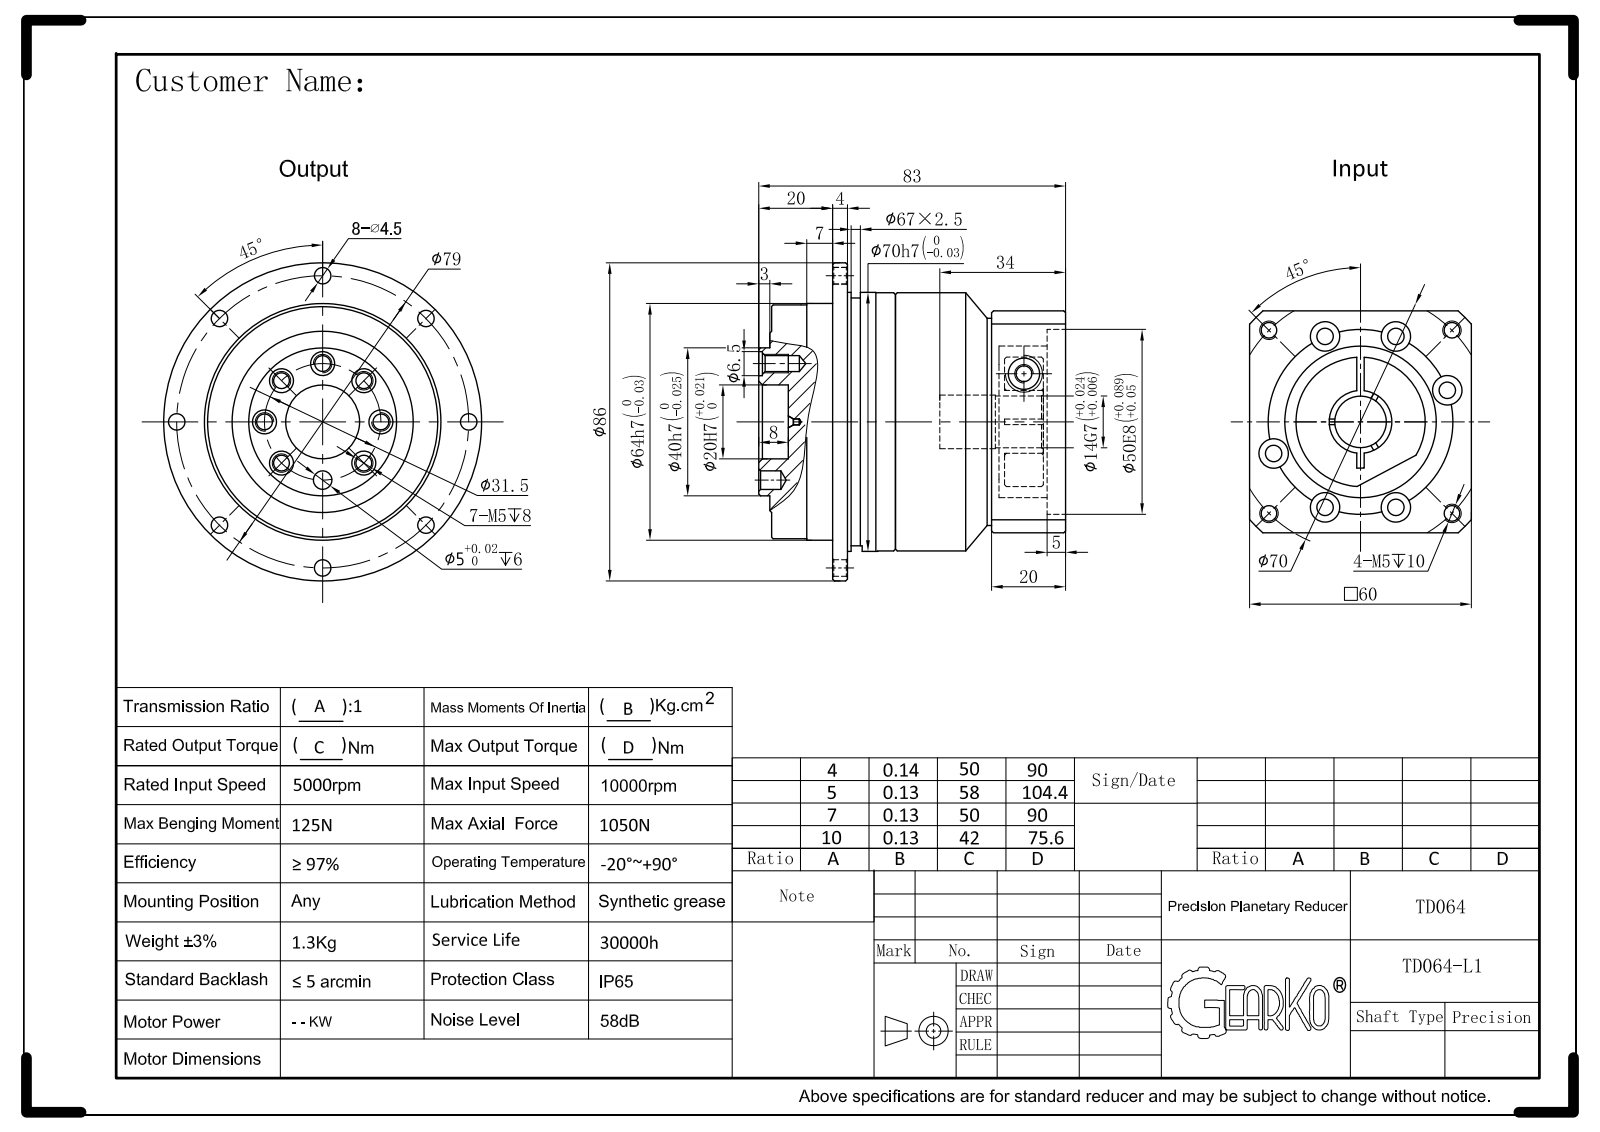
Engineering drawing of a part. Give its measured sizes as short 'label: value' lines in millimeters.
name: TD064-L1-14-50-70-M5-34-5
written by: SolidWorks 2017 (CONFIG_CONTROL_DESIGN)
unit: mm
bodies: 3 solids, 204 faces (40 planar, 88 cylindrical, 76 other)
size: 86 × 86 × 83
volume: 267 132 mm³; area: 44 740 mm²
holes: 11× ⌀4.2, 8× ⌀4.5, 1× ⌀5, 1× ⌀8.5, 1× ⌀9.3, 1× ⌀14, 1× ⌀17, 1× ⌀20, 1× ⌀41, 1× ⌀50, 1× ⌀56
bosses: 1× ⌀86, 1× ⌀70, 1× ⌀69.8, 1× ⌀67, 1× ⌀64, 1× ⌀63.2, 1× ⌀40, 1× ⌀35
rounds: 1× R1, 1× R40
face distances: 63, 60, 45, 16.5, 41, 3.5, 4, 20, 5, 18
hole spacings: 30.47, 42.52, 51.85, 12.06, 15.75, 26.34, 28.81, 29.11
